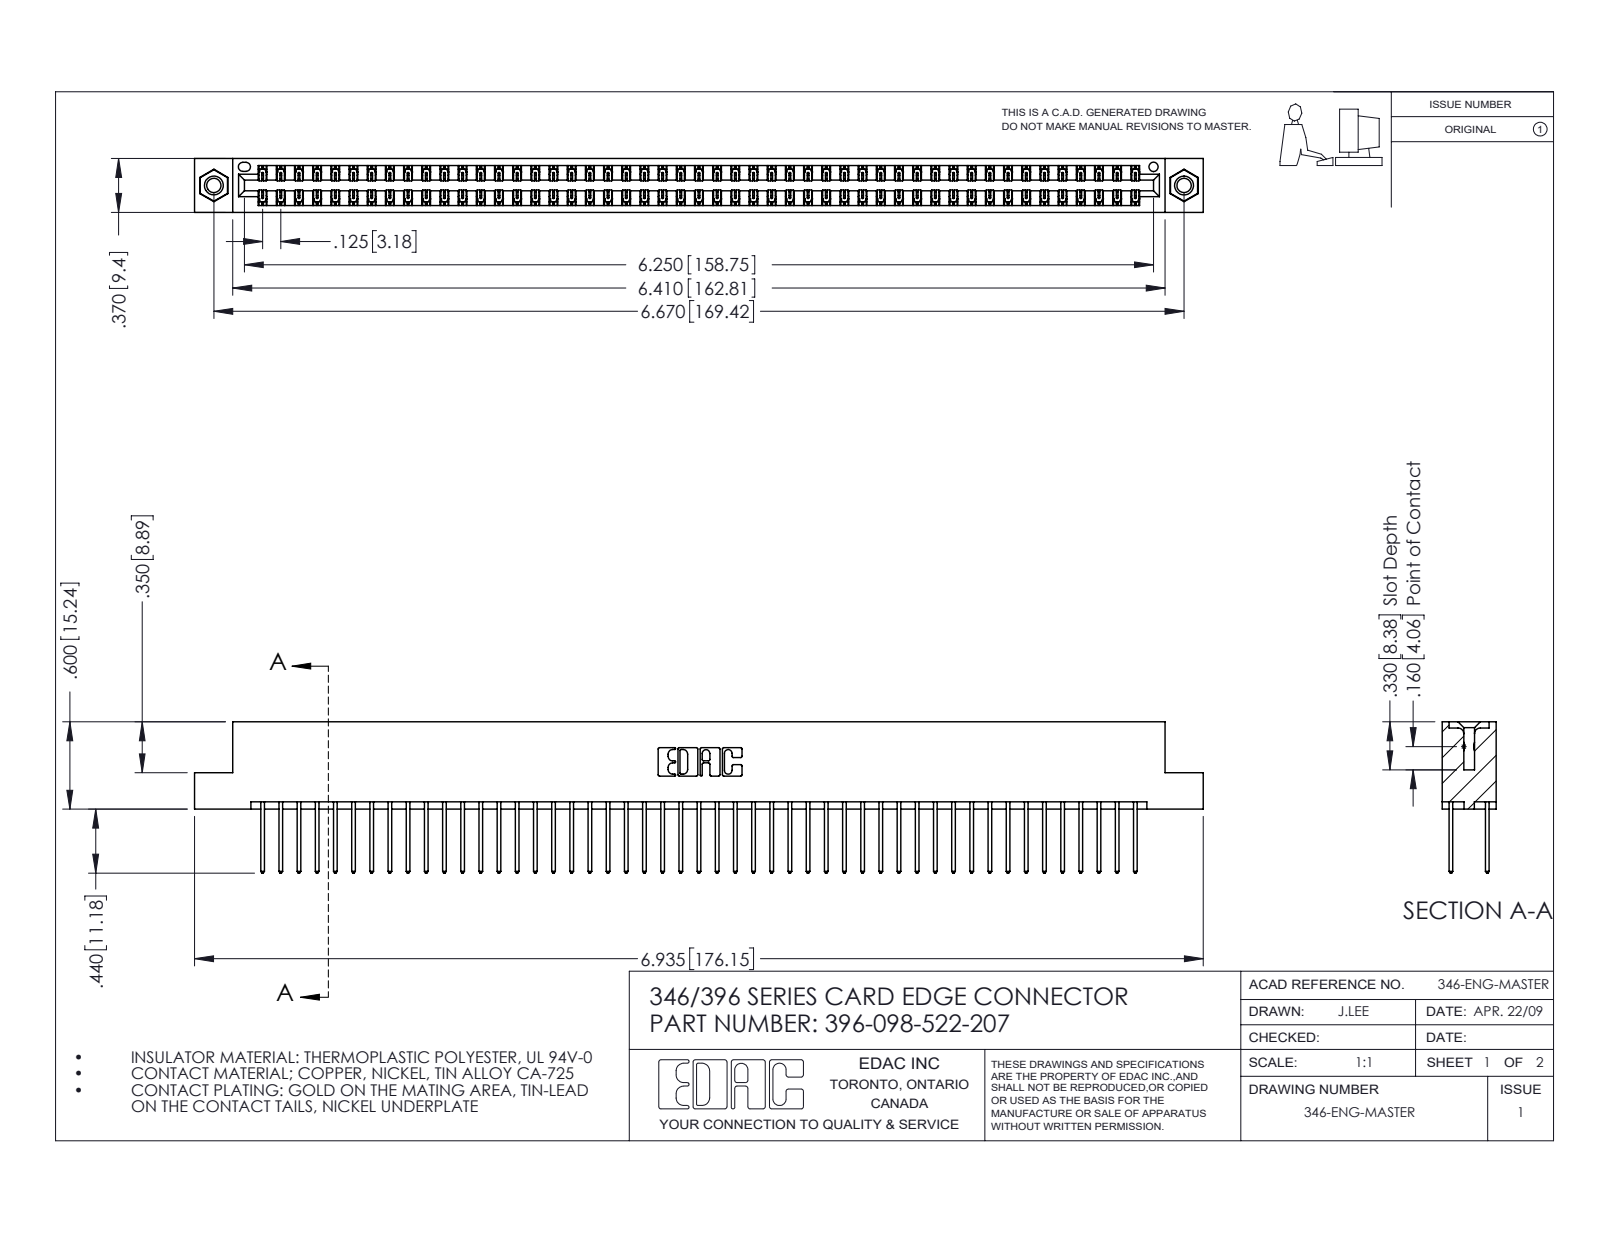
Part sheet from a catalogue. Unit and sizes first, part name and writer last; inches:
Units: inches
Overall size (bounding box): 6.935 × 1.04 × 0.37
Round holes (diameter × count): ⌀0.098 ×2, ⌀0.125 ×2, ⌀0.156 ×2, ⌀0.064 ×1
Round bosses / shafts (diameter × count): ⌀0.155 ×2
Partial cylindrical surfaces — rounded edges, fillets, slot ends (radius × count): R0.006 ×147, R0.01 ×98, R0.01 ×22, R0.007 ×6, R0.031 ×6, R0.026 ×3, R0.014 ×2, R0.022 ×2
Main face-to-face distances: 0.048, 0.322, 0.25, 0.072, 0.298, 0.025, 0.37, 0.275, 0.148, 0.222
Hole centre spacings: 0.246, 6.461, 6.67
Volume: 1.066 in³ · Surface area: 39.25 in²
Bodies: 101 solids, 5278 faces (3538 planar, 1724 cylindrical, 16 other)
Part name (STEP PRODUCT): 346 Part_Flush Mounting Lugs - 0.156 Dia-TI; 345-292-001_345-293-122; 396-098-522-207; 345-250-001_345-250-005-103
STEP written by: SolidWorks 2016 (CONFIG_CONTROL_DESIGN)
